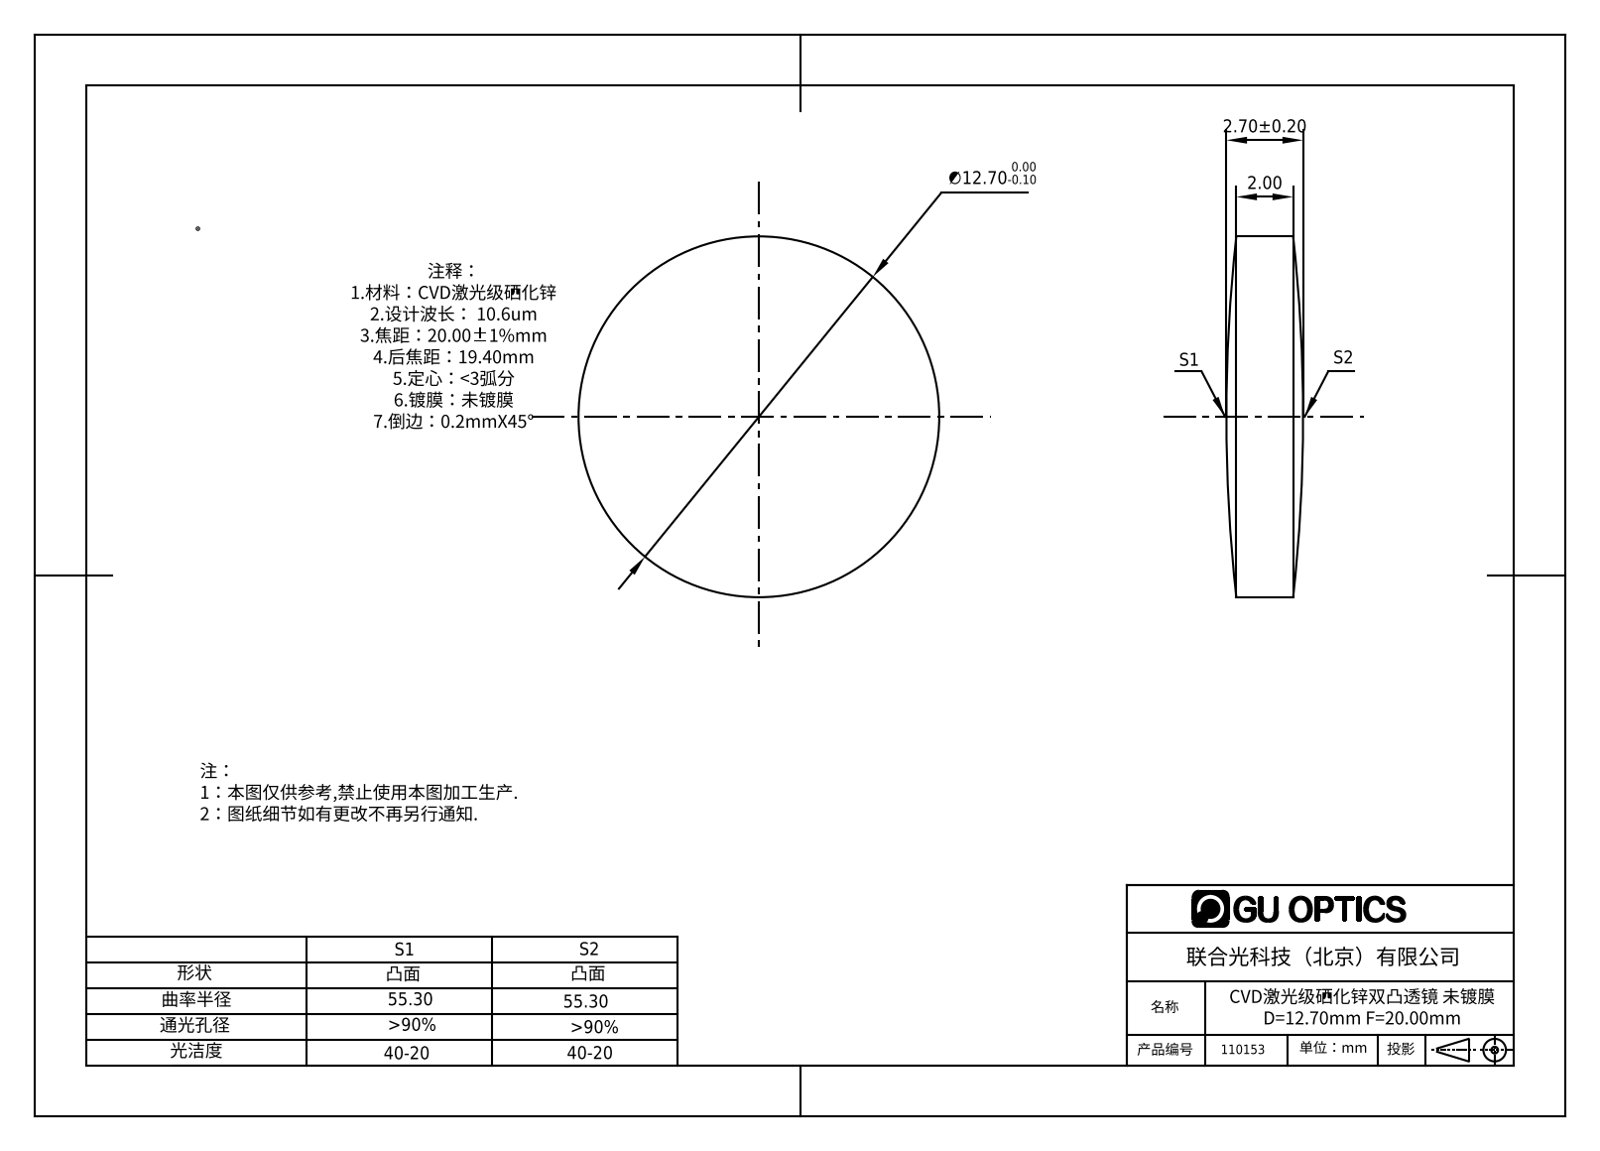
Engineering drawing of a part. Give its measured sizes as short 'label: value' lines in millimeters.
name: 110153
written by: SolidWorks 2016 (CONFIG_CONTROL_DESIGN)
unit: mm
bodies: 1 solid, 6 faces (0 planar, 2 cylindrical, 4 other)
size: 12.7 × 12.7 × 2.7
volume: 298 mm³; area: 334 mm²
bosses: 1× ⌀12.7
